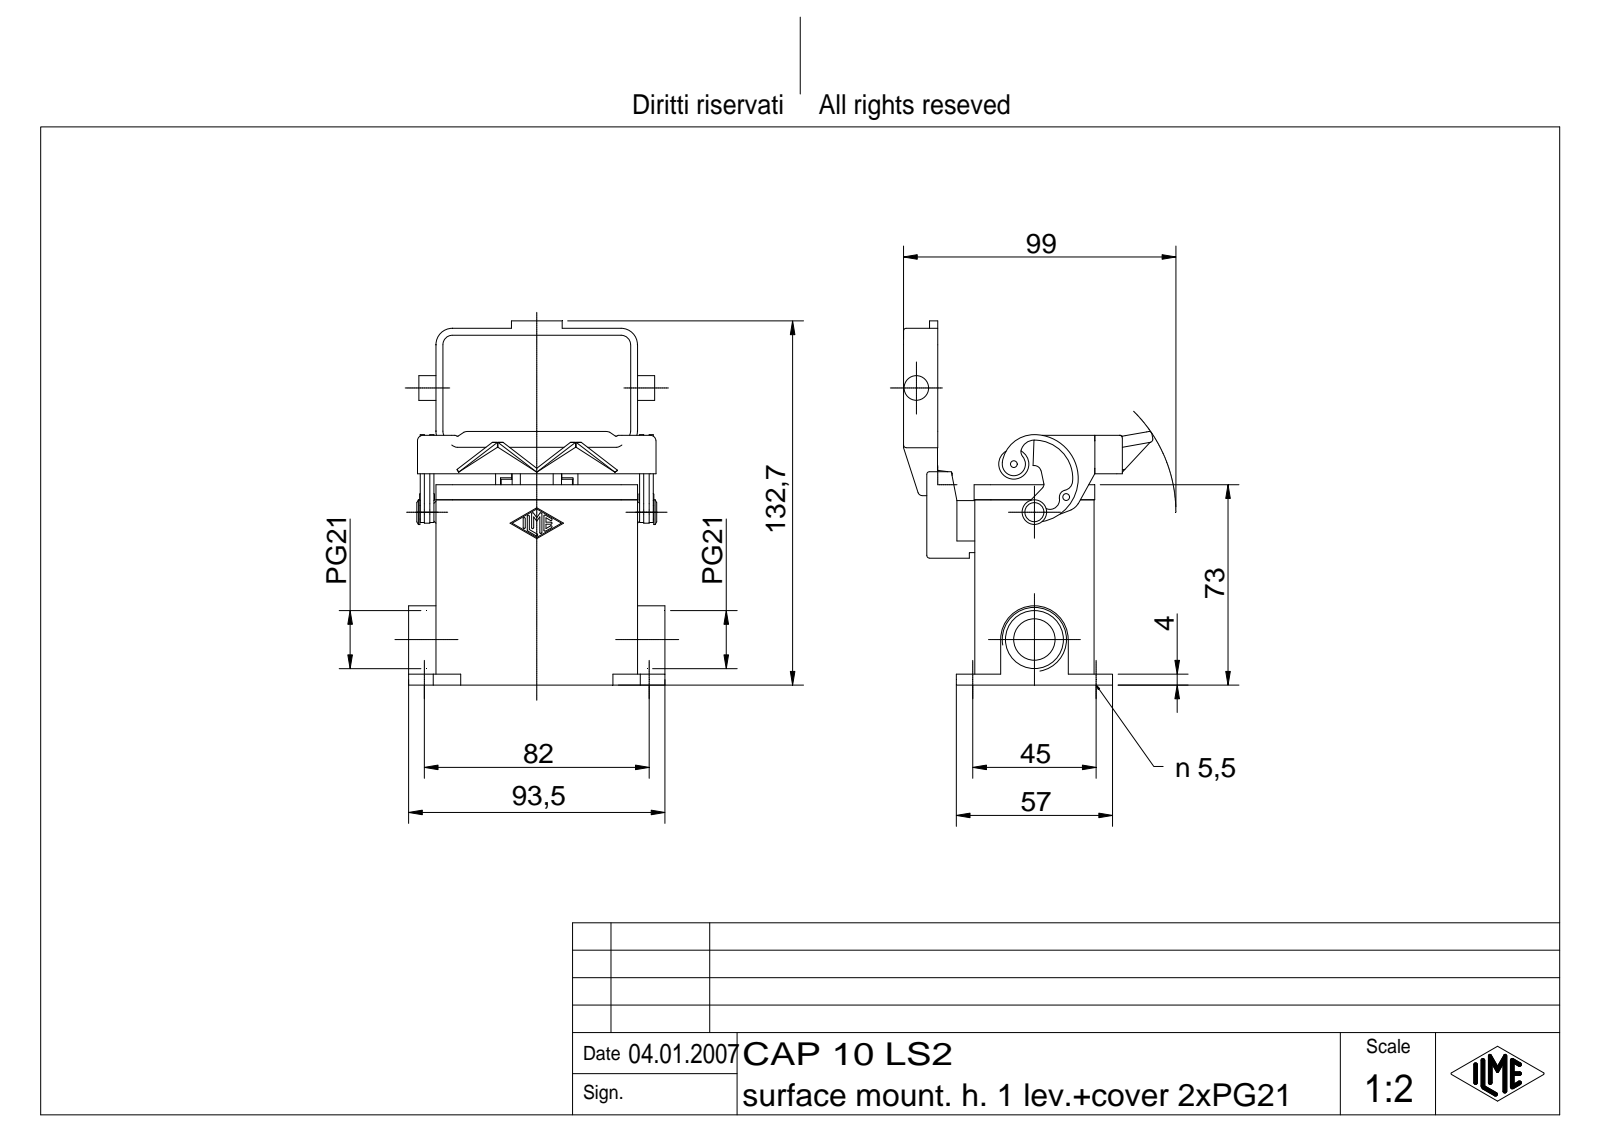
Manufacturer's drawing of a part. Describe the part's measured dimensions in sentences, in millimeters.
The part is named "CAP 10 LS2". Its 3-D file was written by "Autodesk Inventor 7 (AUTOMOTIVE_DESIGN)". It is 6 solids with 591 faces: 251 planar, 180 cylindrical and 160 other. Overall it measures 132.7 by 93.5 by 90.95 millimeters. Its volume is 133 731 cubic millimeters and its surface area 70 380 square millimeters. Round holes: 4 of diameter 5.5, 1 of diameter 2, 1 of diameter 4, 1 of diameter 15.16, 1 of diameter 21.16. Round bosses or shafts: 2 of diameter 9, 2 of diameter 5, 1 of diameter 11, 1 of diameter 7, 1 of diameter 4, 1 of diameter 3, 1 of diameter 2.5. Partial cylindrical surfaces (rounded edges, fillets, slot ends): 18 of radius 1, 14 of radius 0.38, 12 of radius 2, 12 of radius 6, 6 of radius 1.5, 6 of radius 3.5, 4 of radius 3, 3 of radius 0.5. The main face-to-face distances are 3, 40.5, 4, 43.5, 26, 37.5, 66.5, 61.75, 69.5, 29. The hole center spacings are 45, 82, 93.54, 53.2.
